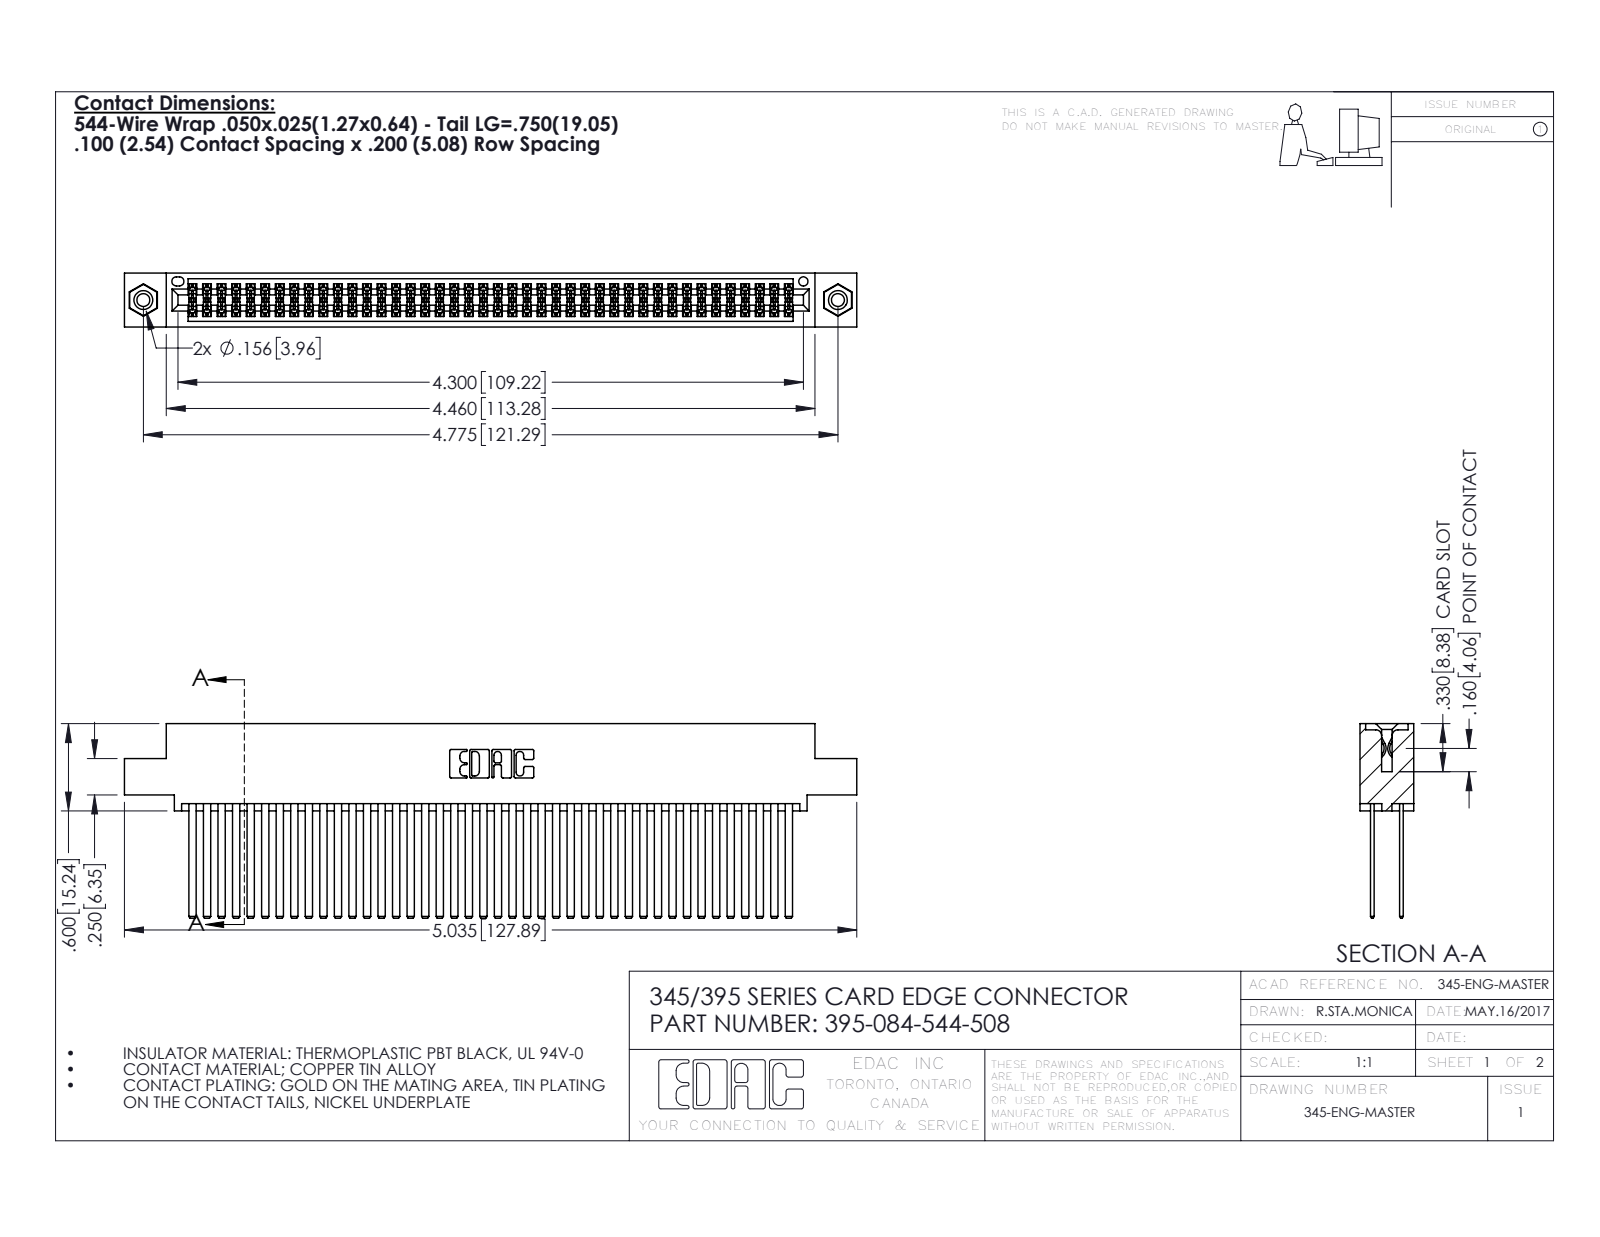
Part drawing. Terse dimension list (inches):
name: 345-292-001_345-293-144; 345 Part_0.110 Offset - 0.156 Dia-TI; 345-250-001_345-250-003-102; 395-084-544-508
written by: SolidWorks 2016 (CONFIG_CONTROL_DESIGN)
unit: in
bodies: 87 solids, 3886 faces (2552 planar, 1318 cylindrical, 16 other)
size: 5.035 × 1.337 × 0.37
volume: 0.825 in³; area: 36.49 in²
holes: 2× ⌀0.089, 2× ⌀0.125, 2× ⌀0.156, 1× ⌀0.064
bosses: 2× ⌀0.155
rounds: 126× R0.006, 22× R0.01, 6× R0.007, 6× R0.031, 3× R0.026, 2× R0.014, 2× R0.019, 2× R0.022
face distances: 0.2, 0.025, 0.072, 0.098, 0.272, 0.298, 0.225, 0.175, 0.37, 0.05
hole spacings: 0.27, 4.539, 4.775
